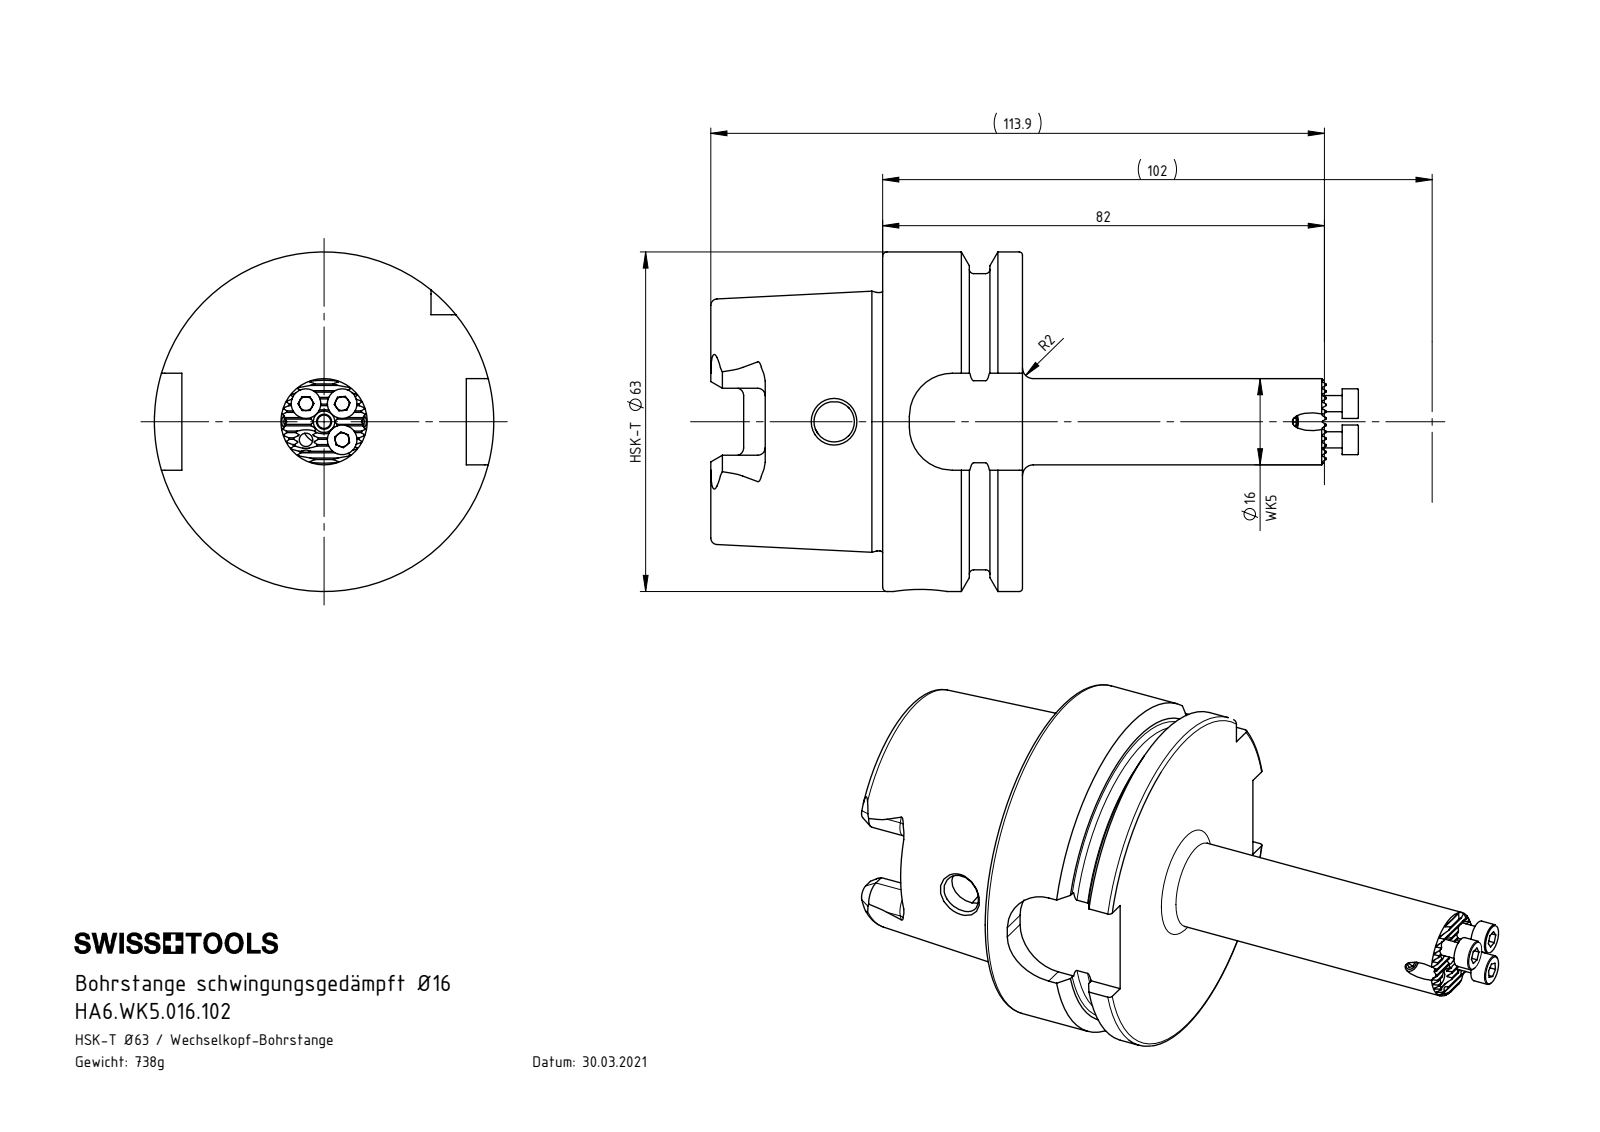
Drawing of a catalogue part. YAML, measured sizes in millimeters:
part_name: "WK5-ER1.010.002_A_aufgebohrt; WK5-ER1.009.047_A_Fertigbearbeitung; HA6.WK5.016.102; ISO 4026 - M3 x 3 (+2 more)"
step_written_by: "SolidWorks 2022 (CONFIG_CONTROL_DESIGN)"
units: millimeters
bodies: {solids: 8, faces: 477, planar: 194, cylindrical: 141, other: 142}
overall_size: [120.2, 63, 63]
volume: 91790
surface_area: 29735
round_holes:
  - {diameter: 2.5, count: 7}
  - {diameter: 3.3, count: 2}
  - {diameter: 3, count: 1}
  - {diameter: 4, count: 1}
  - {diameter: 5.4, count: 1}
  - {diameter: 7.5, count: 1}
  - {diameter: 8.4, count: 1}
  - {diameter: 9.5, count: 1}
  - {diameter: 10, count: 1}
  - {diameter: 17, count: 1}
  - {diameter: 19, count: 1}
  - {diameter: 34, count: 1}
round_bosses_or_shafts:
  - {diameter: 3, count: 5}
  - {diameter: 5.5, count: 3}
  - {diameter: 63, count: 1}
  - {diameter: 54.95, count: 1}
  - {diameter: 47.94, count: 1}
  - {diameter: 16, count: 1}
  - {diameter: 9, count: 1}
partial_cylinders:
  - {radius: 0.12, count: 13}
  - {radius: 1.4, count: 6}
  - {radius: 2.88, count: 4}
  - {radius: 8, count: 4}
face_to_face_distances: [25.95, 16, 9.95, 31.9, 41.85, 57.85, 52.8, 21.8, 11.85, 53.7]
hole_center_spacings: [4.75, 6.72, 9.5]
